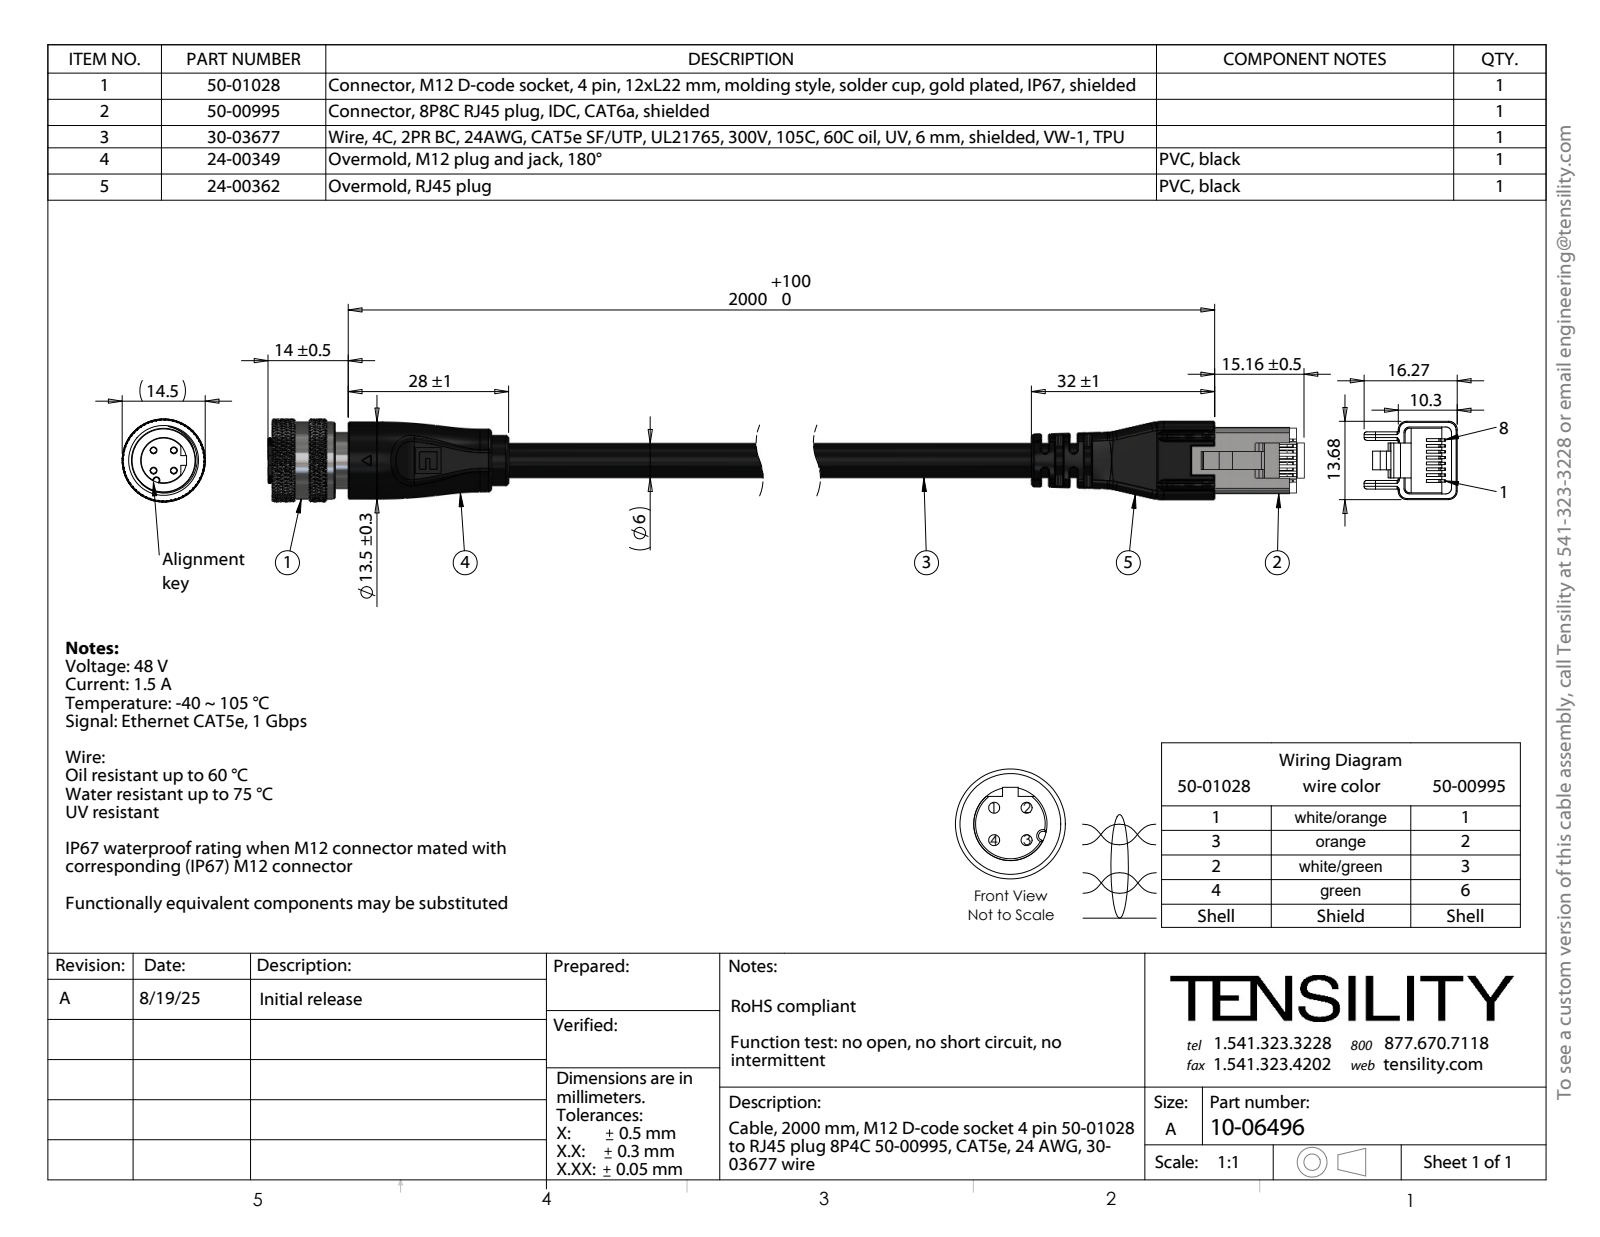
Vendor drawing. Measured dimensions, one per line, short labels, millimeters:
name: 50-01028-04_默认; 50-01028-05_默认; 24-00362; 50-01028_默认 (+7 more)
written by: SolidWorks 2025 (CONFIG_CONTROL_DESIGN)
unit: mm
bodies: 55 solids, 3967 faces (546 planar, 928 cylindrical, 2493 other)
size: 229.11 × 18.37 × 14.5
volume: 14 248 mm³; area: 29 704 mm²
holes: 28× ⌀0.2, 4× ⌀1.05, 4× ⌀1.1, 4× ⌀1.2, 1× ⌀3.16, 1× ⌀3.21, 1× ⌀3.56, 1× ⌀9, 1× ⌀10, 1× ⌀11.2
bosses: 4× ⌀1.6, 4× ⌀1.5, 1× ⌀13.5, 1× ⌀11, 1× ⌀10.6, 1× ⌀10.5, 1× ⌀9.8, 1× ⌀9.7
rounds: 11× R0.2, 10× R0.1, 10× R0.5, 10× R1.5, 8× R0.62, 6× R0.4, 5× R1, 4× R10
face distances: 1.25, 1, 2.5, 3.75, 9.3, 5, 1.5, 199.5, 12.68, 8.5
hole spacings: 1.91, 0.36, 2.09, 1.06, 0.89, 1.08, 1.24, 1.8
